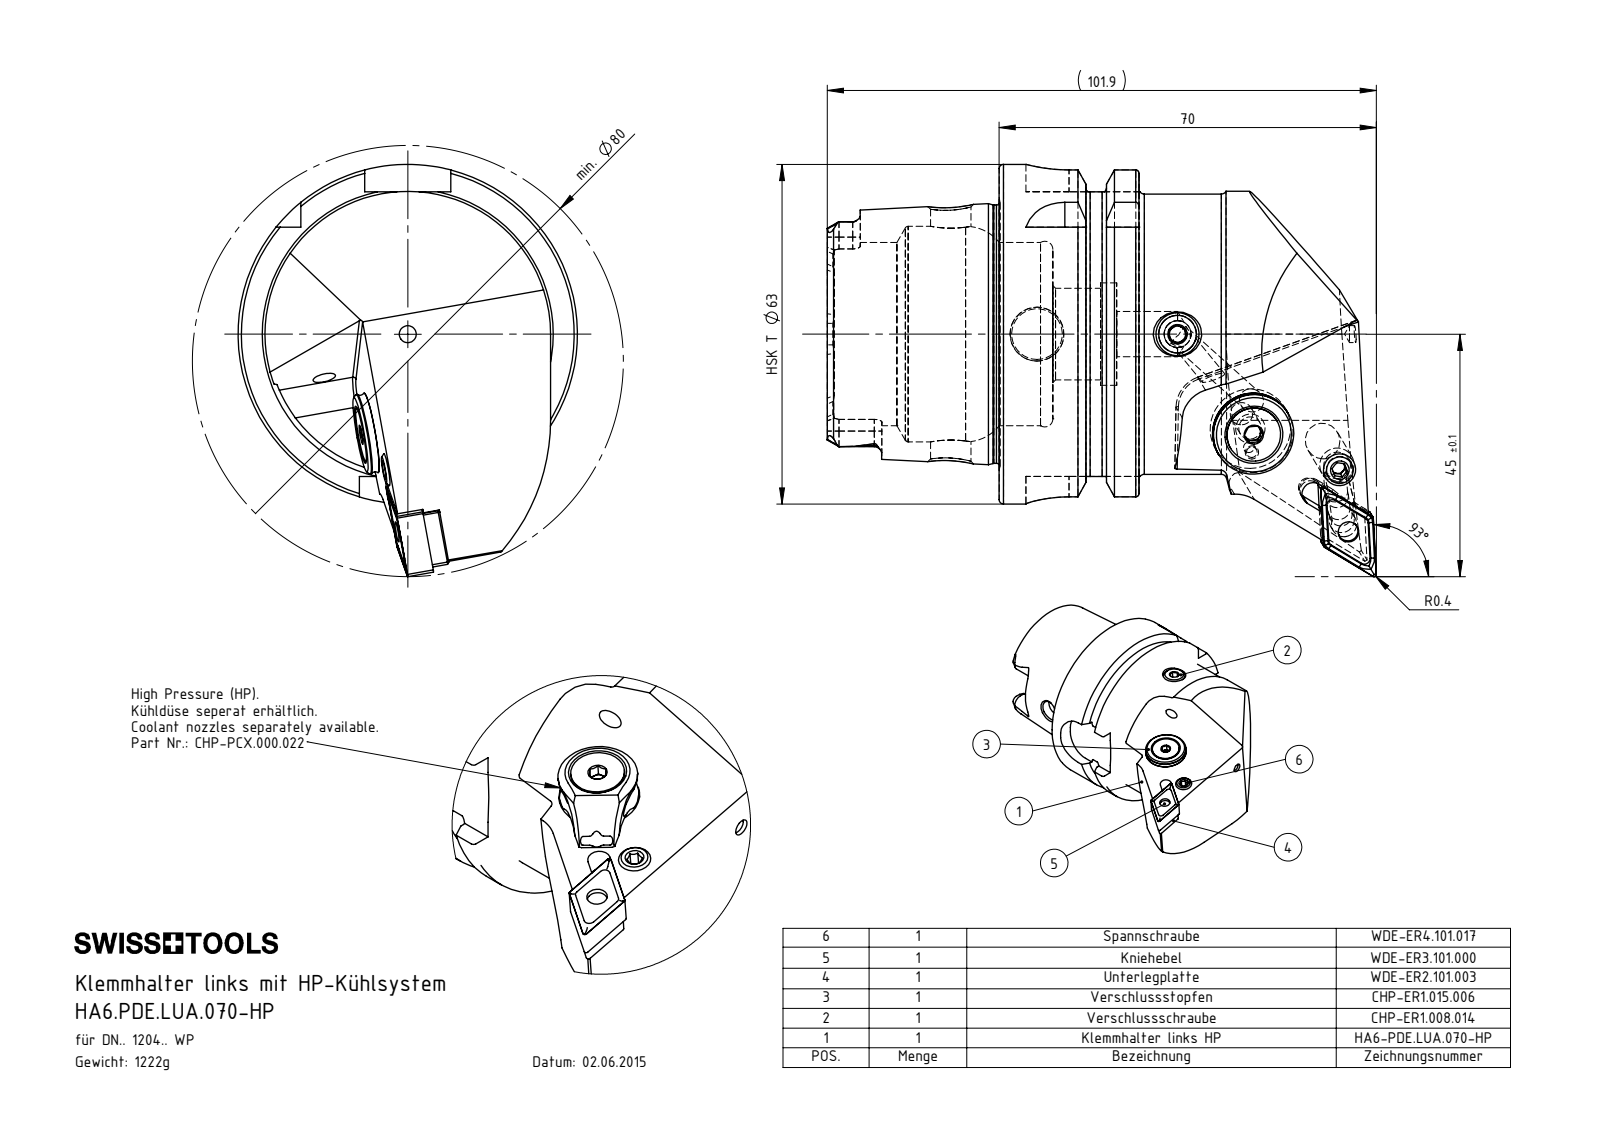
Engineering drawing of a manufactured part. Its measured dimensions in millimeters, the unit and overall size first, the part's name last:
Units: millimetres
Overall size (bounding box): 101.91 × 76.5 × 63
Round holes (diameter × count): ⌀4.2 ×3, ⌀2.5 ×2, ⌀5 ×2, ⌀1.2 ×1, ⌀2 ×1, ⌀3 ×1, ⌀3.15 ×1, ⌀3.81 ×1, ⌀4.8 ×1, ⌀5.2 ×1, ⌀6.4 ×1, ⌀7 ×1
Round bosses / shafts (diameter × count): ⌀63 ×1, ⌀54.95 ×1, ⌀52 ×1, ⌀47.94 ×1, ⌀15 ×1, ⌀13.4 ×1, ⌀10 ×1, ⌀8 ×1
Partial cylindrical surfaces — rounded edges, fillets, slot ends (radius × count): R0.4 ×8, R1.4 ×6, R2.1 ×5, R2.88 ×4, R8 ×4, R0.5 ×2, R1.83 ×1, R1.85 ×1
Main face-to-face distances: 25.95, 16, 9.95, 31.9, 41.85, 57.85, 52.8, 21.8, 11.85, 4.5
Hole centre spacings: 4.51, 16.14, 17.75, 22.71, 4.5, 4.52, 11.79, 11.8
Volume: 155 830 mm³ · Surface area: 35 066 mm²
Bodies: 11 solids, 398 faces (176 planar, 87 cylindrical, 135 other)
Part name (STEP PRODUCT): DNMG110404; WDE-ER3.101.000_A; WDE-ER1.101.000; WDE-ER2.101.003_A (+8 more)
STEP written by: SolidWorks 2017 (AUTOMOTIVE_DESIGN)
